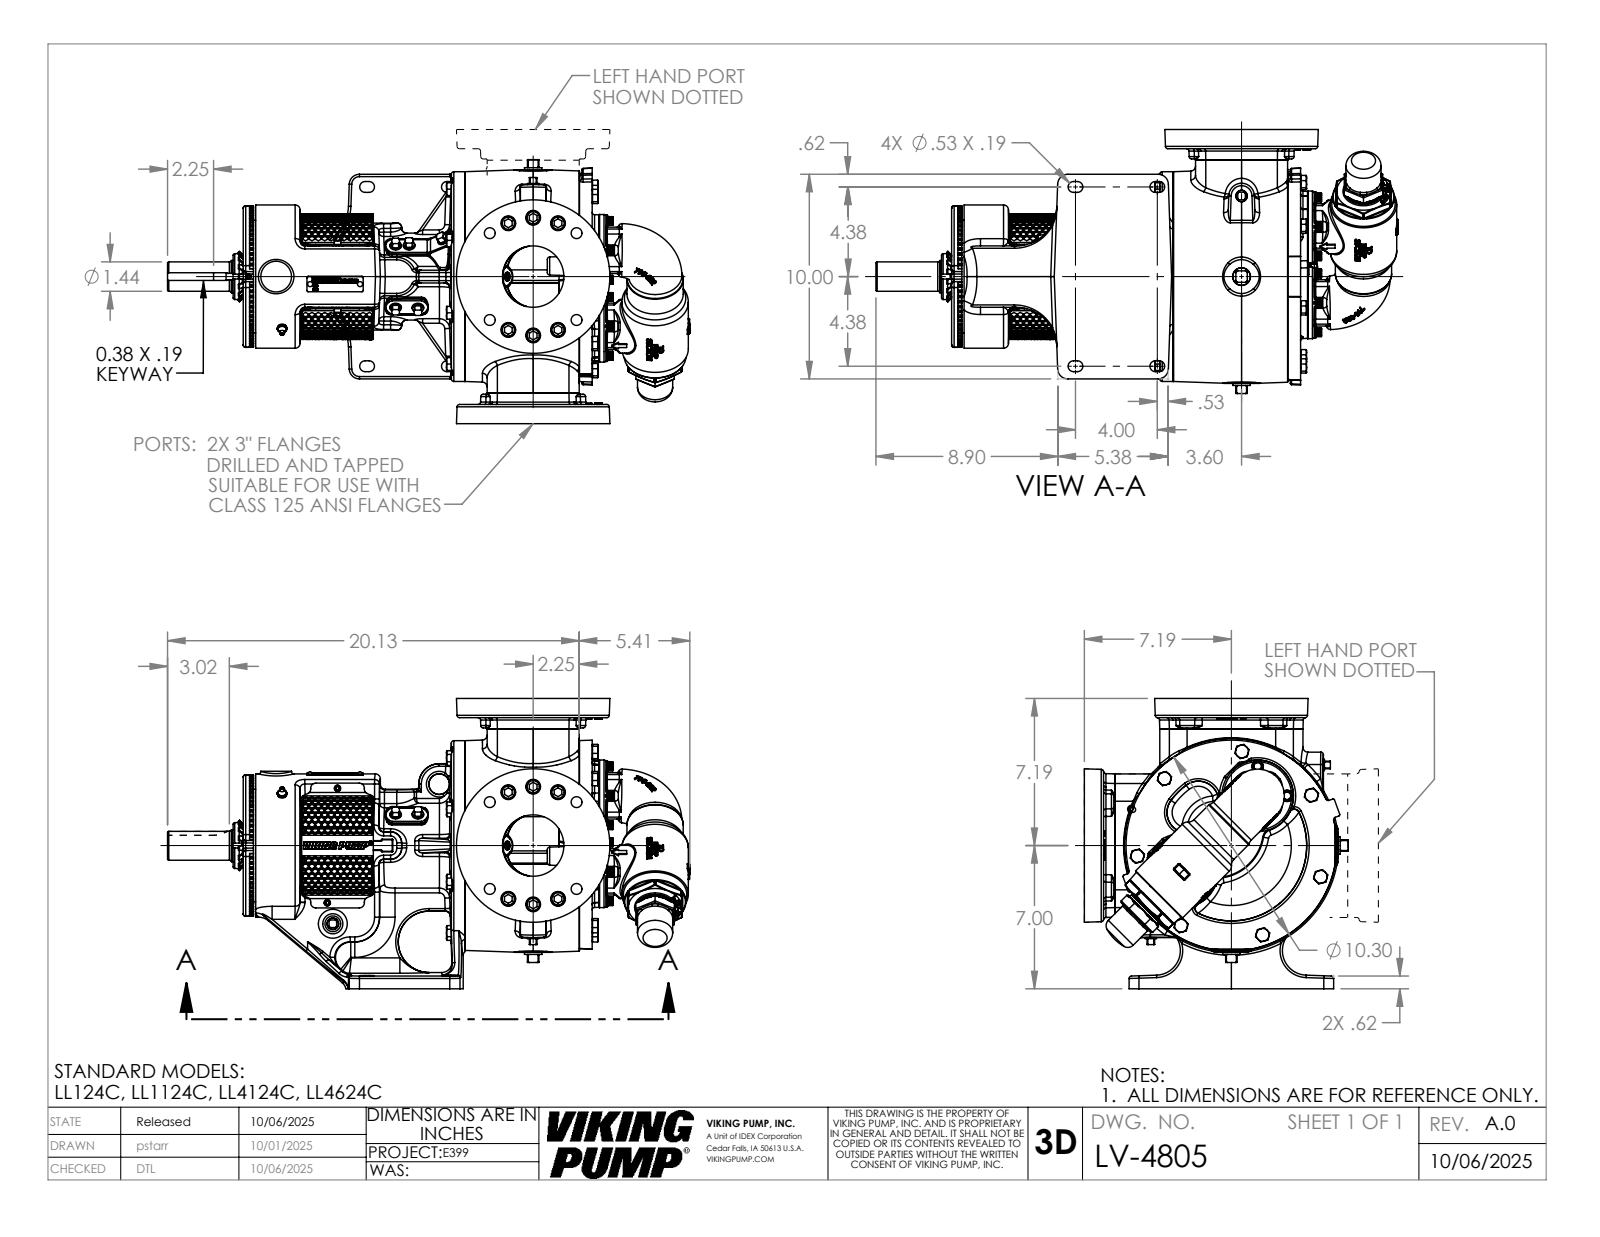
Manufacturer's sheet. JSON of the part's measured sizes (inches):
{"part_name": "LV-4805", "step_written_by": "SolidWorks 2024 (AUTOMOTIVE_DESIGN)", "units": "inches", "bodies": {"solids": 1, "faces": 6477, "planar": 2047, "cylindrical": 1224, "other": 3206}, "overall_size": [25.533, 14.187, 12.902], "volume_in3": 1063, "surface_area_in2": 1486, "round_holes": [[0.719, 12], [0.25, 9], [0.531, 8], [1.094, 8], [0.199, 6], [0.159, 3], [0.266, 2], [0.313, 2], [3, 2], [0.453, 1], [1.552, 1], [1.578, 1]], "round_bosses_or_shafts": [[0.66, 12], [0.625, 10], [0.563, 8], [0.625, 5], [0.312, 3], [0.19, 3], [3.5, 2], [10.25, 1]], "partial_cylinders_radius": [[0.063, 109], [0.12, 80], [0.069, 74], [0.01, 66], [0.24, 48], [0.03, 36], [0.06, 16], [0.45, 16]], "face_to_face_distances": [14.187, 10.77, 3.54, 14.31, 0.5, 2.25, 0.94, 0.403, 1.343, 2.14], "hole_center_spacings": [3, 4.243, 2.875, 1.375, 1.028, 1.244, 2.18, 2.251]}
